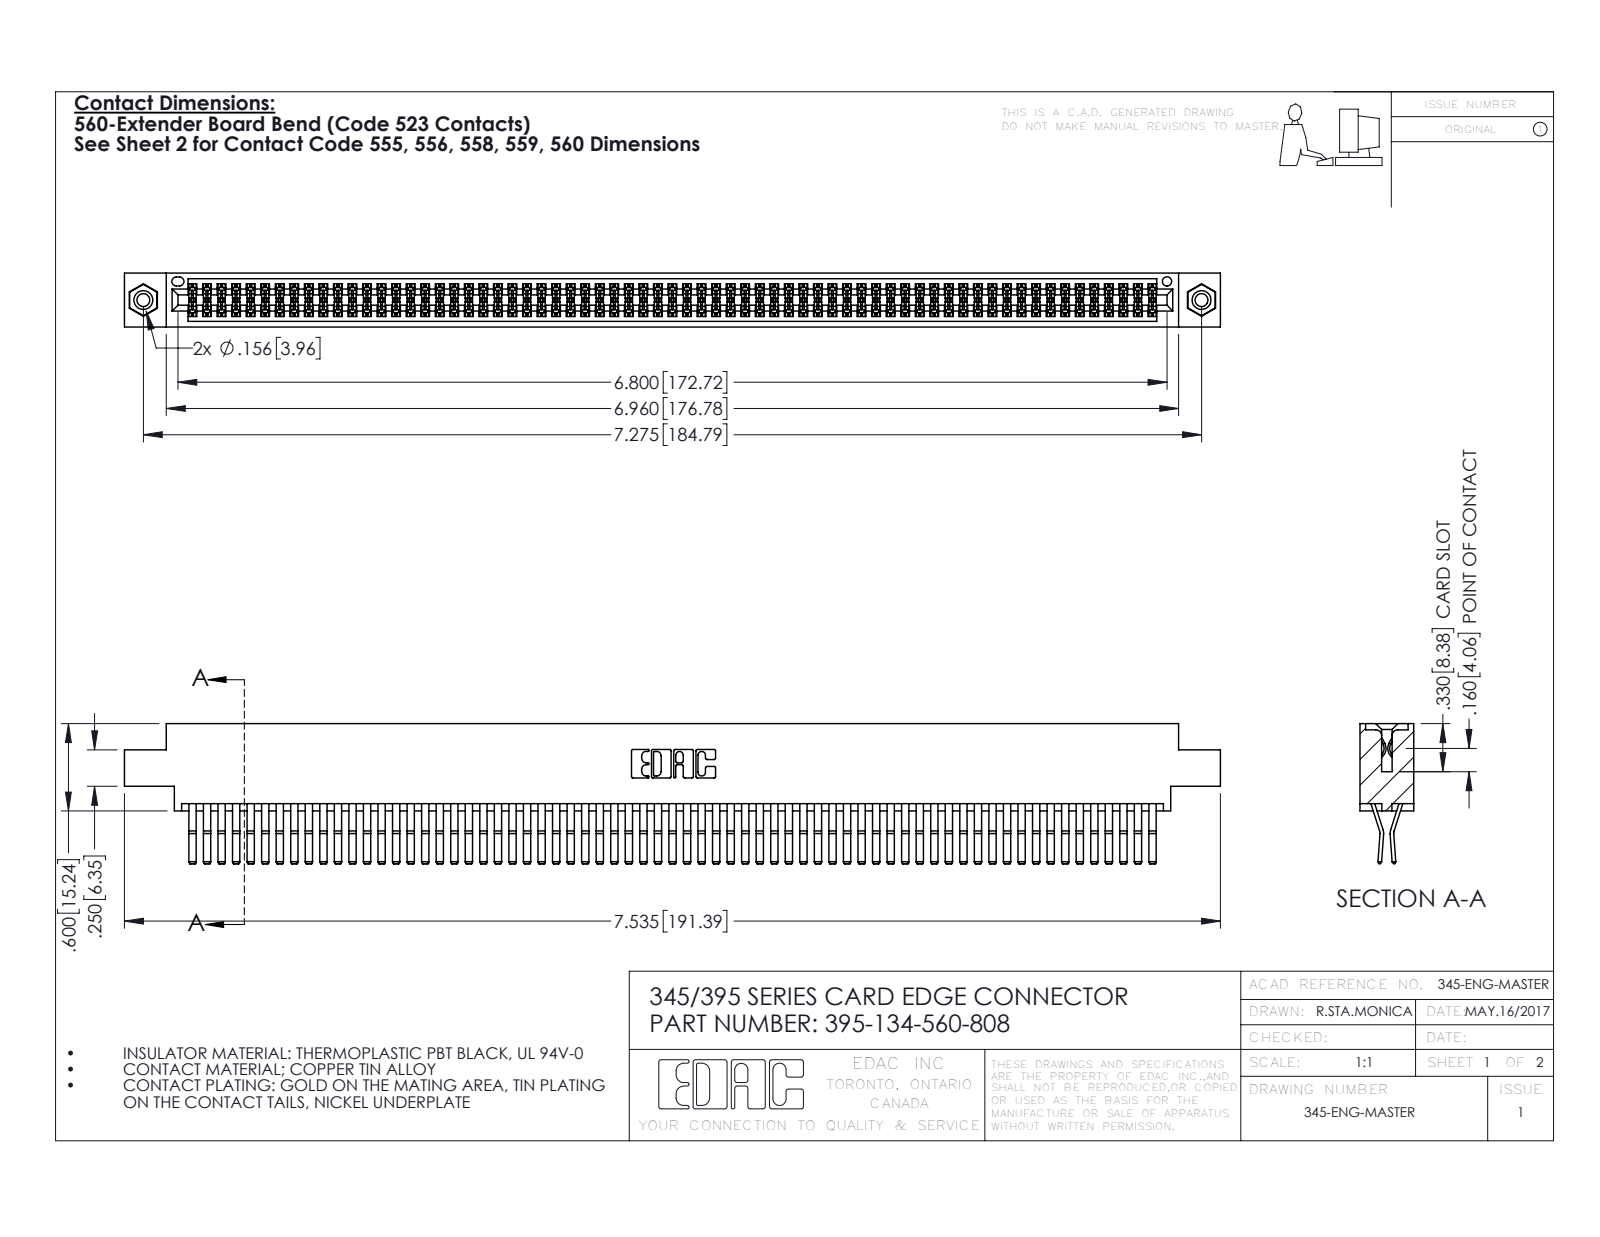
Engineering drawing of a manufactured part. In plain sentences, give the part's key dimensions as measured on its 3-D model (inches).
The part is named "345-250-001_345-250-003-102; 395-134-560-808; 345 Part_0.170 Offset - 0.156 Dia-TI; 345-292-001_560 Tail". Its 3-D file was written by "SolidWorks 2016 (CONFIG_CONTROL_DESIGN)". It is 137 solids with 7158 faces: 4538 planar, 2604 cylindrical and 16 other. Overall it measures 7.535 by 0.962 by 0.37 inches. Its volume is 1.195 cubic inches and its surface area 49.36 square inches. Round holes: 2 of diameter 0.089, 2 of diameter 0.125, 2 of diameter 0.156, 1 of diameter 0.064. Round bosses or shafts: 2 of diameter 0.155. Partial cylindrical surfaces (rounded edges, fillets, slot ends): 201 of radius 0.006, 22 of radius 0.01, 6 of radius 0.007, 6 of radius 0.031, 3 of radius 0.026, 2 of radius 0.01, 2 of radius 0.014, 2 of radius 0.019. The main face-to-face distances are 0.025, 0.072, 0.298, 0.37, 0.2, 0.098, 0.272, 0.225, 0.175, 0.149. The hole center spacings are 0.27, 7.039, 7.275.
